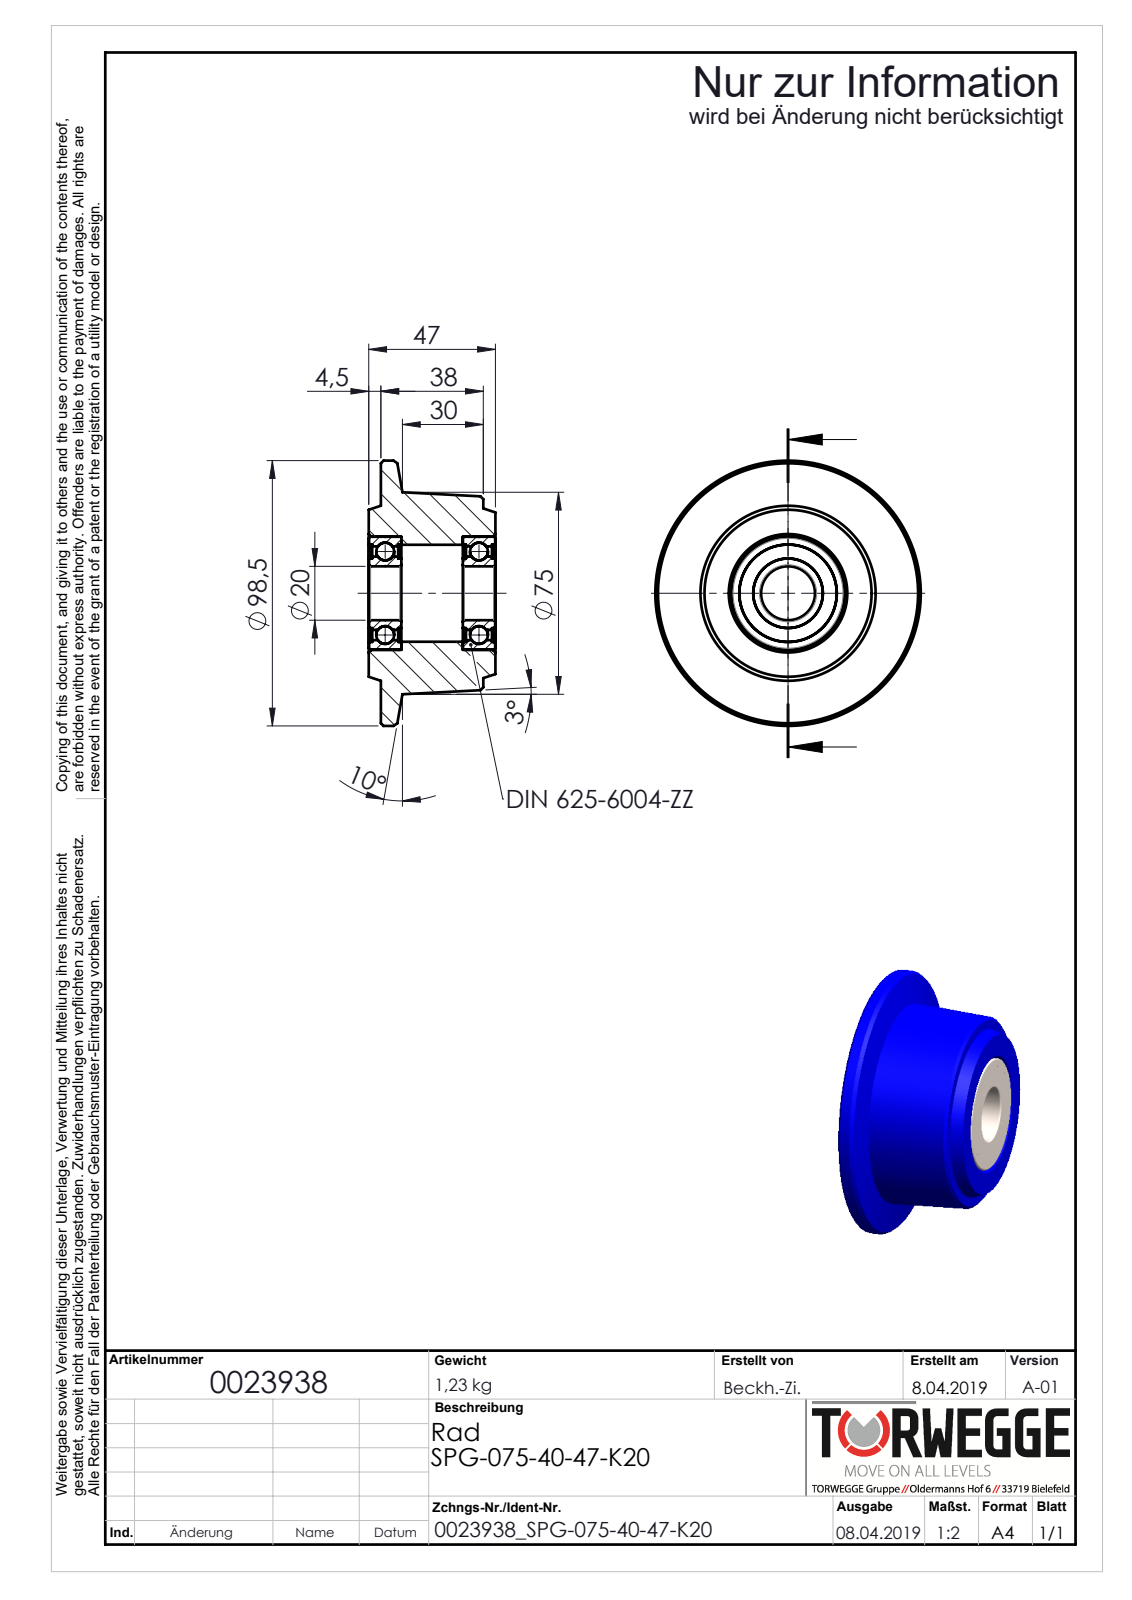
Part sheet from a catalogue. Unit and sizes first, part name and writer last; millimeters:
Units: millimetres
Overall size (bounding box): 98.5 × 98.5 × 47
Round holes (diameter × count): ⌀20 ×1, ⌀25.83 ×1, ⌀34.83 ×1, ⌀36 ×1, ⌀36.17 ×1, ⌀42 ×1
Round bosses / shafts (diameter × count): ⌀98.5 ×1, ⌀27.17 ×1
Main face-to-face distances: 34.8, 34.9, 12.1, 4.5, 30.4, 7.6, 42.5, 0.59, 11.41, 46.9
Volume: 176 755 mm³ · Surface area: 48 901 mm²
Bodies: 11 solids, 148 faces (30 planar, 64 cylindrical, 54 other)
Part name (STEP PRODUCT): 0023938_SPG-075-40-47-K20_(A-01)
STEP written by: SolidWorks 2018 (AUTOMOTIVE_DESIGN)
